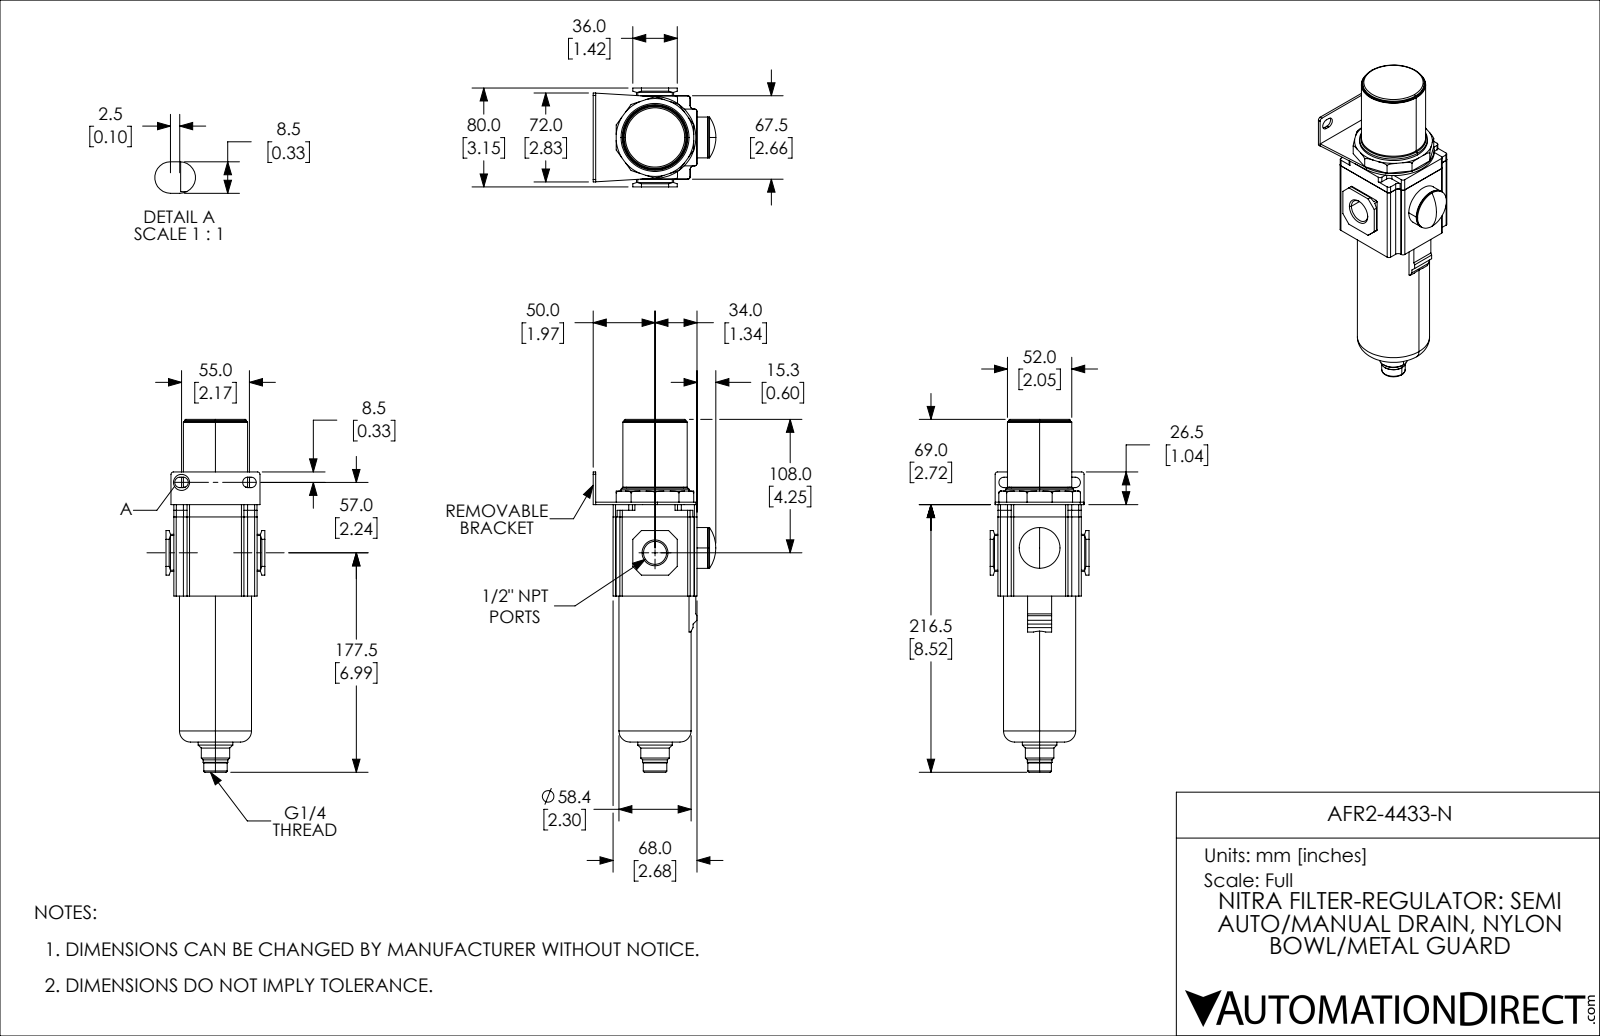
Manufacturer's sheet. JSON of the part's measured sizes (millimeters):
{"part_name": "AFR2-4433-N", "step_written_by": "SolidWorks 2019 (CONFIG_CONTROL_DESIGN)", "units": "millimeters", "bodies": {"solids": 1, "faces": 222, "planar": 119, "cylindrical": 67, "other": 36}, "overall_size": [285.5, 99.28, 80], "volume_mm3": 822072, "surface_area_mm2": 76004, "round_holes": [[11.45, 1], [18.63, 1]], "round_bosses_or_shafts": [[58.4, 1], [55, 1], [52, 1], [50, 1], [45.9, 1], [33, 1], [28, 1], [23, 1]], "partial_cylinders_radius": [[2, 22], [3, 12], [4.25, 4], [33, 1]], "face_to_face_distances": [2, 67.5, 67, 68, 16, 69, 84, 6.25, 73.75, 76]}
